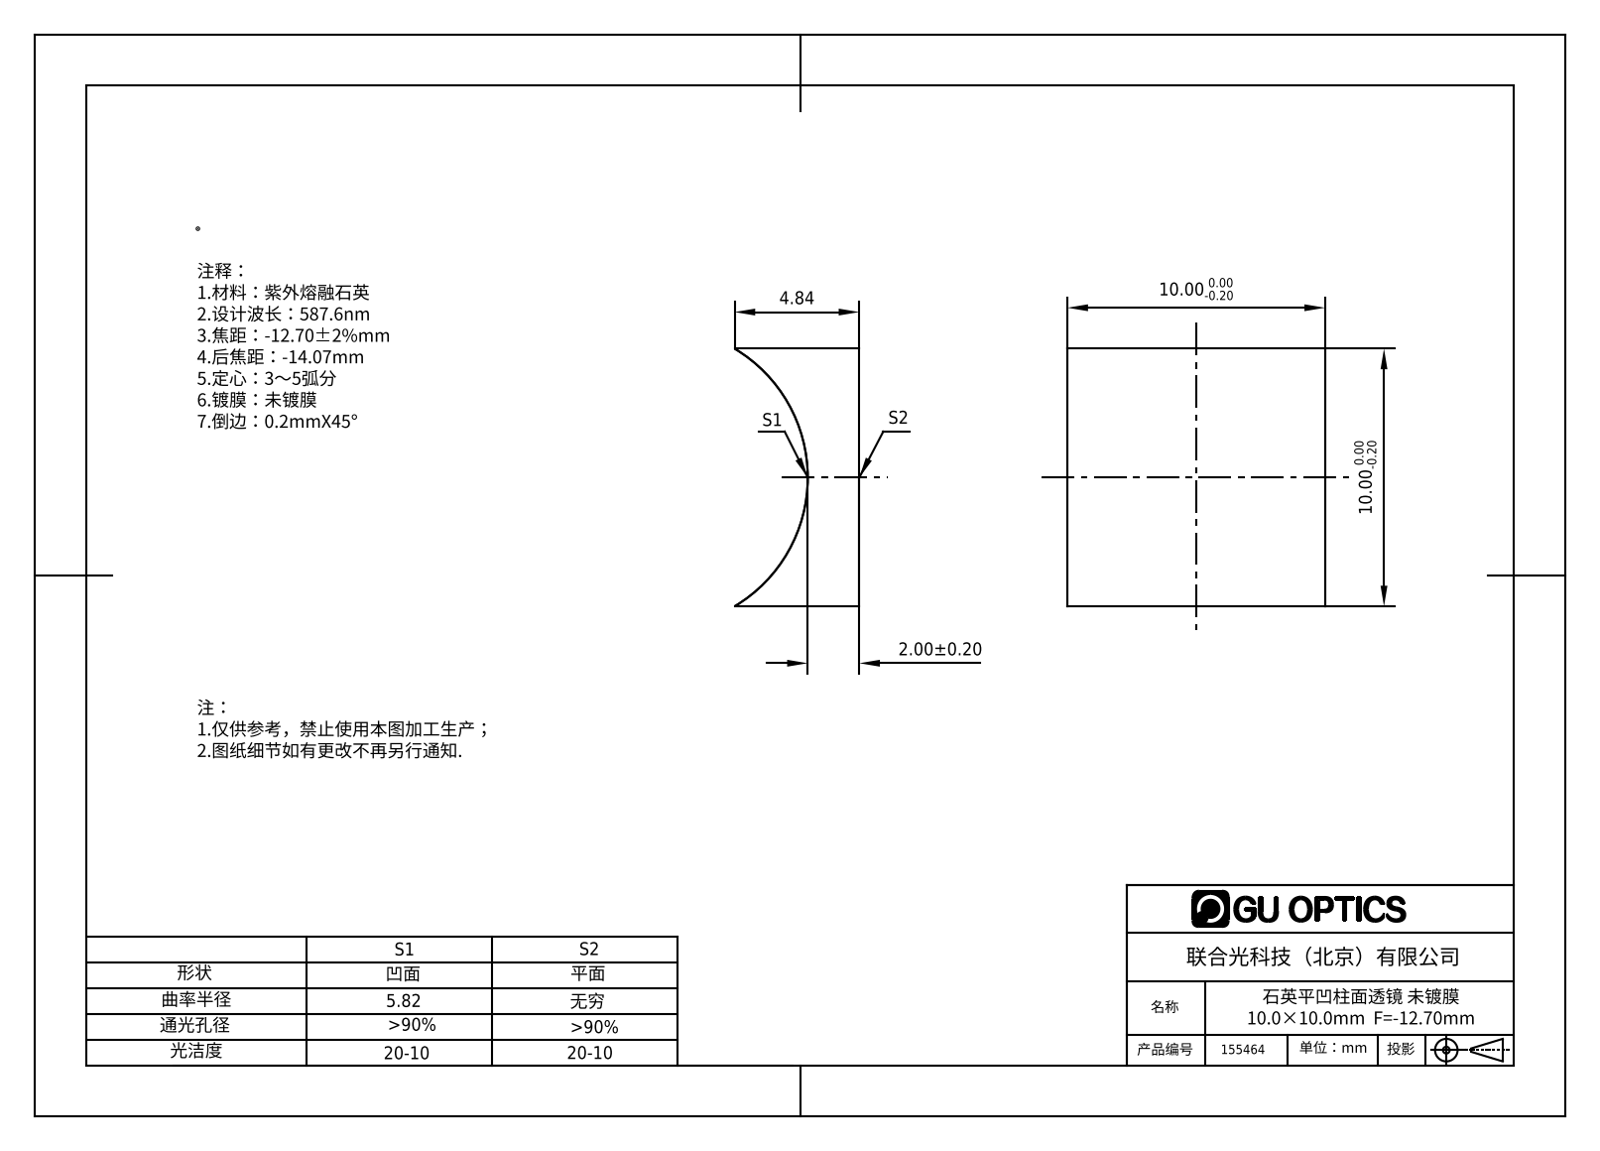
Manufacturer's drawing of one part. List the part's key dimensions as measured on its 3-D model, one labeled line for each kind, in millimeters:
Part name (STEP PRODUCT): 155464
STEP written by: SolidWorks 2016 (AUTOMOTIVE_DESIGN)
Units: millimetres
Bodies: 1 solid, 6 faces (5 planar, 1 cylindrical, 0 other)
Overall size (bounding box): 10 × 10 × 4.84
Volume: 283 mm³ · Surface area: 374 mm²
Partial cylindrical surfaces — rounded edges, fillets, slot ends (radius × count): R5.82 ×1
Main face-to-face distances: 10
